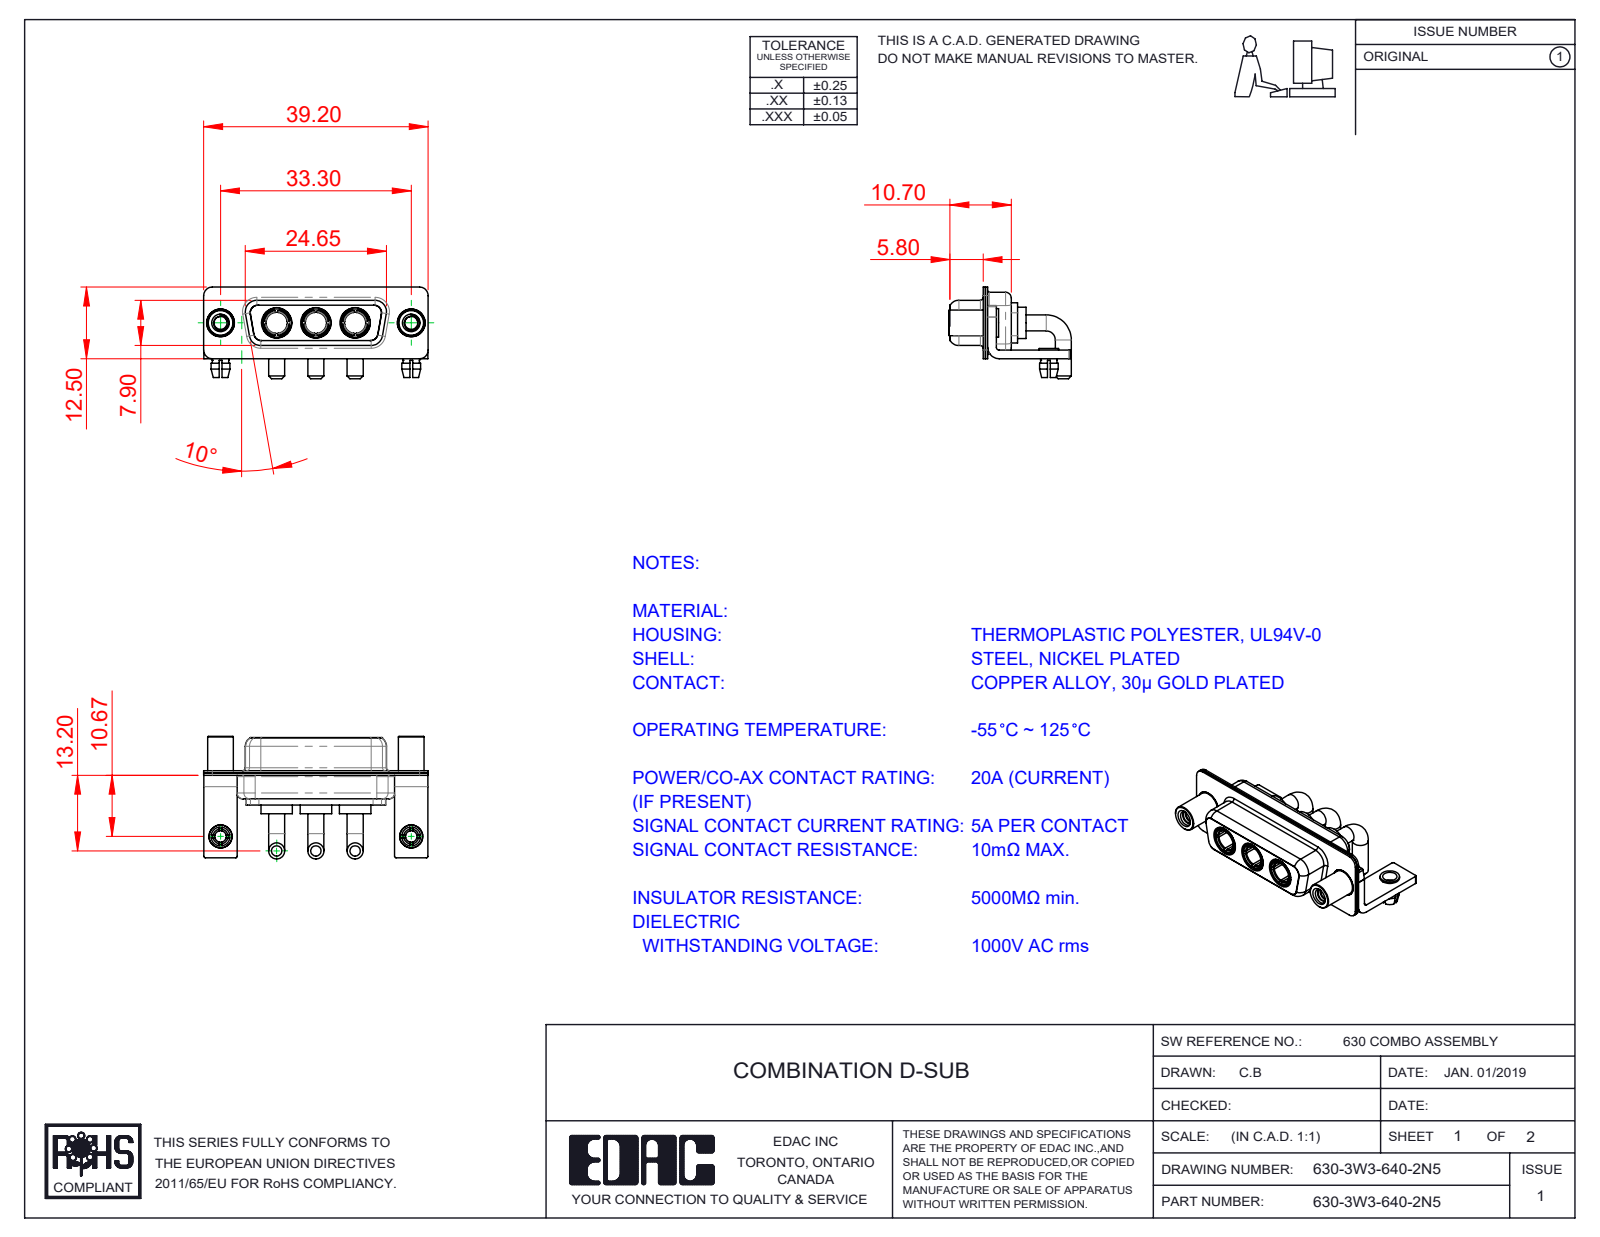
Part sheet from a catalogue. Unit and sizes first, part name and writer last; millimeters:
Units: millimetres
Overall size (bounding box): 39.2 × 21.4 × 16
Round holes (diameter × count): ⌀4.85 ×5, ⌀3.7 ×3, ⌀5.3 ×3, ⌀2 ×2, ⌀2.26 ×2, ⌀2.5 ×2, ⌀3.2 ×2, ⌀4 ×2, ⌀4.05 ×2
Round bosses / shafts (diameter × count): ⌀2.8 ×6, ⌀5.5 ×3, ⌀5.2 ×3, ⌀4.96 ×3, ⌀4.75 ×3, ⌀3.75 ×3, ⌀5 ×2, ⌀4.95 ×2
Partial cylindrical surfaces — rounded edges, fillets, slot ends (radius × count): R0.25 ×16, R1.5 ×16, R2 ×13, R1.35 ×12, R1.6 ×8, R0.5 ×5, R0.6 ×4, R0.65 ×4
Main face-to-face distances: 0.4, 0.8, 1.4, 1.5, 0.45, 8.45, 1.8, 8.9, 5.2, 7.05
Hole centre spacings: 6.85, 9.8, 16.65, 23.5, 33.3, 13.7
Volume: 3 075 mm³ · Surface area: 7 050 mm²
Bodies: 15 solids, 693 faces (224 planar, 304 cylindrical, 165 other)
Part name (STEP PRODUCT): Power Socket_20A RA; 630Combo Shell Front_15 Contacts; 630Combo Shell Rear_15 Contacts; 630-3W3-640-2N5 (+4 more)
STEP written by: SolidWorks 2020 (CONFIG_CONTROL_DESIGN)
